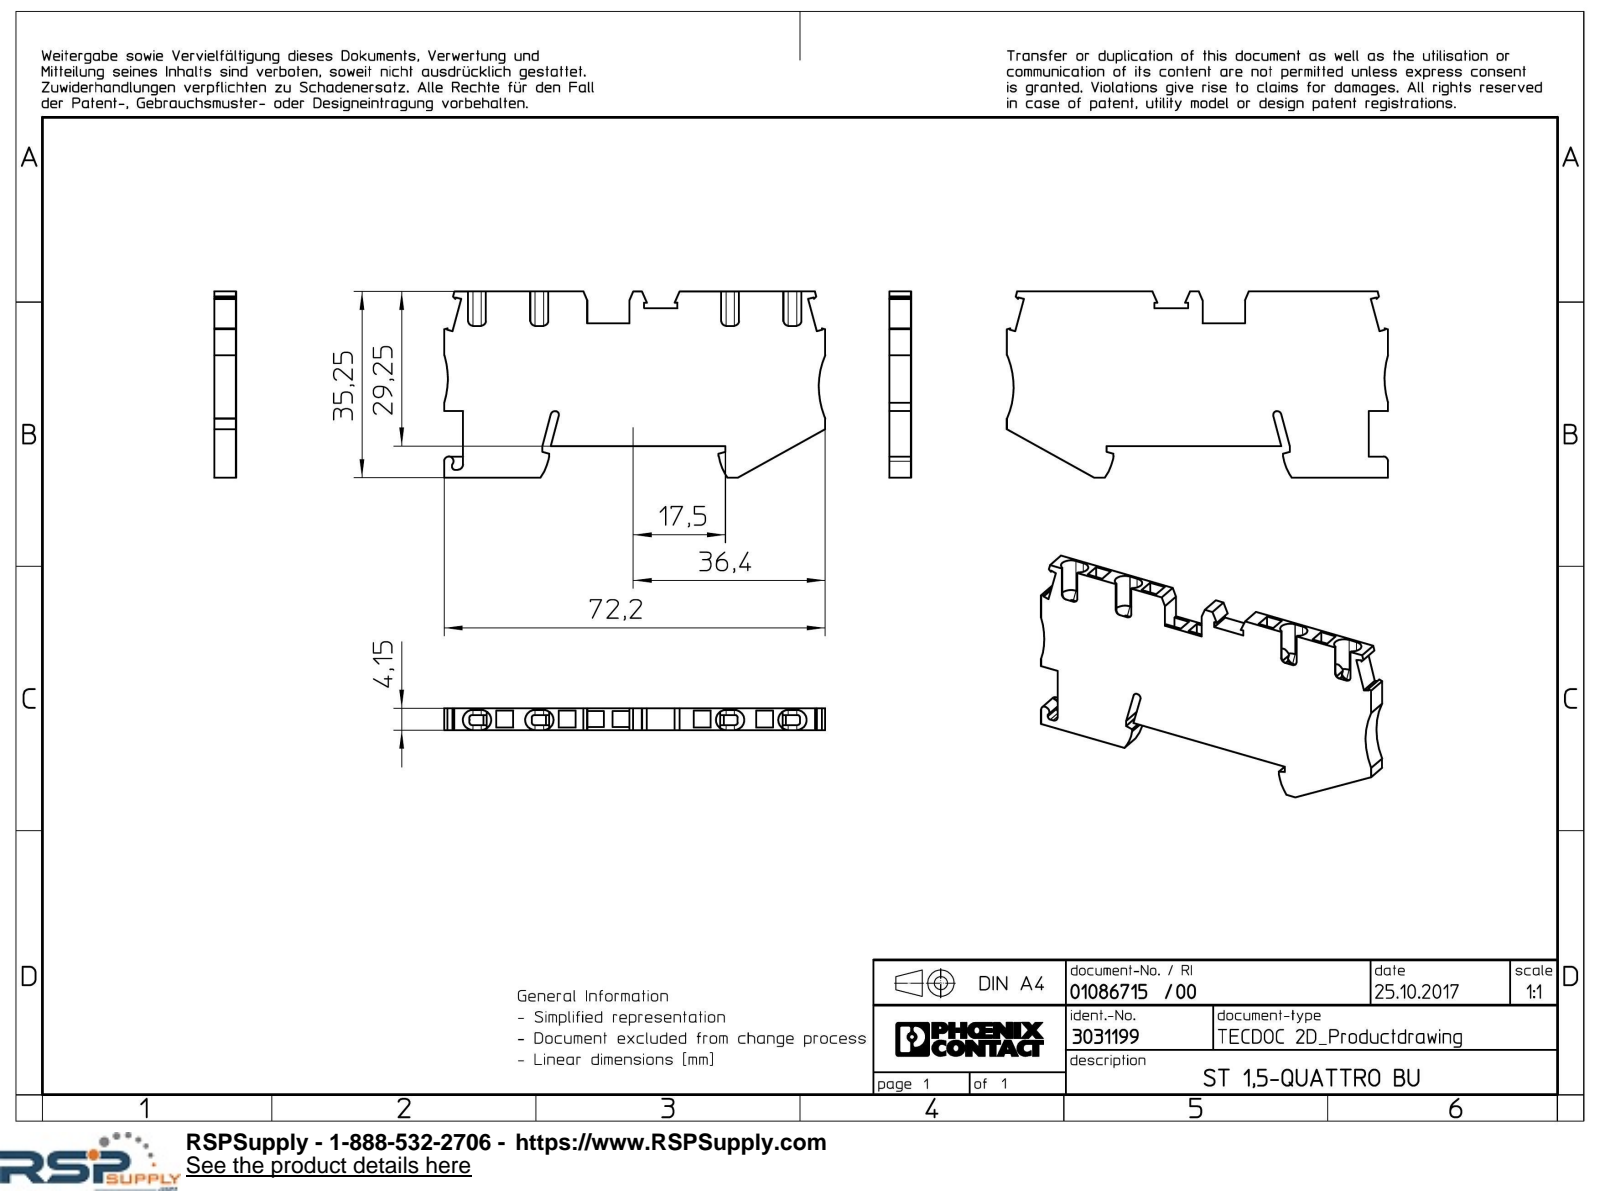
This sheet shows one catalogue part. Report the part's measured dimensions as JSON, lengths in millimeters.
{"part_name": "st_1.5quattro_bu_select", "step_written_by": "Creo Elements/Direct Modeling 20.1A 29-Sep-2018 (C) Parametric Technology GmbH (AUTOMOTIVE_DESIGN)", "units": "millimeters", "bodies": {"solids": 1, "faces": 185, "planar": 140, "cylindrical": 33, "other": 12}, "overall_size": [72.2, 35.25, 4.15], "volume_mm3": 7527, "surface_area_mm2": 6571, "partial_cylinders_radius": [[0.5, 9], [0.9, 9], [1.9, 8], [9.5, 2], [15, 2], [0.7, 1], [0.8, 1], [1, 1]], "face_to_face_distances": [4.15, 3.2, 0.45, 11.8, 2.85, 29.25, 0.95, 6, 0.5, 3.65]}
